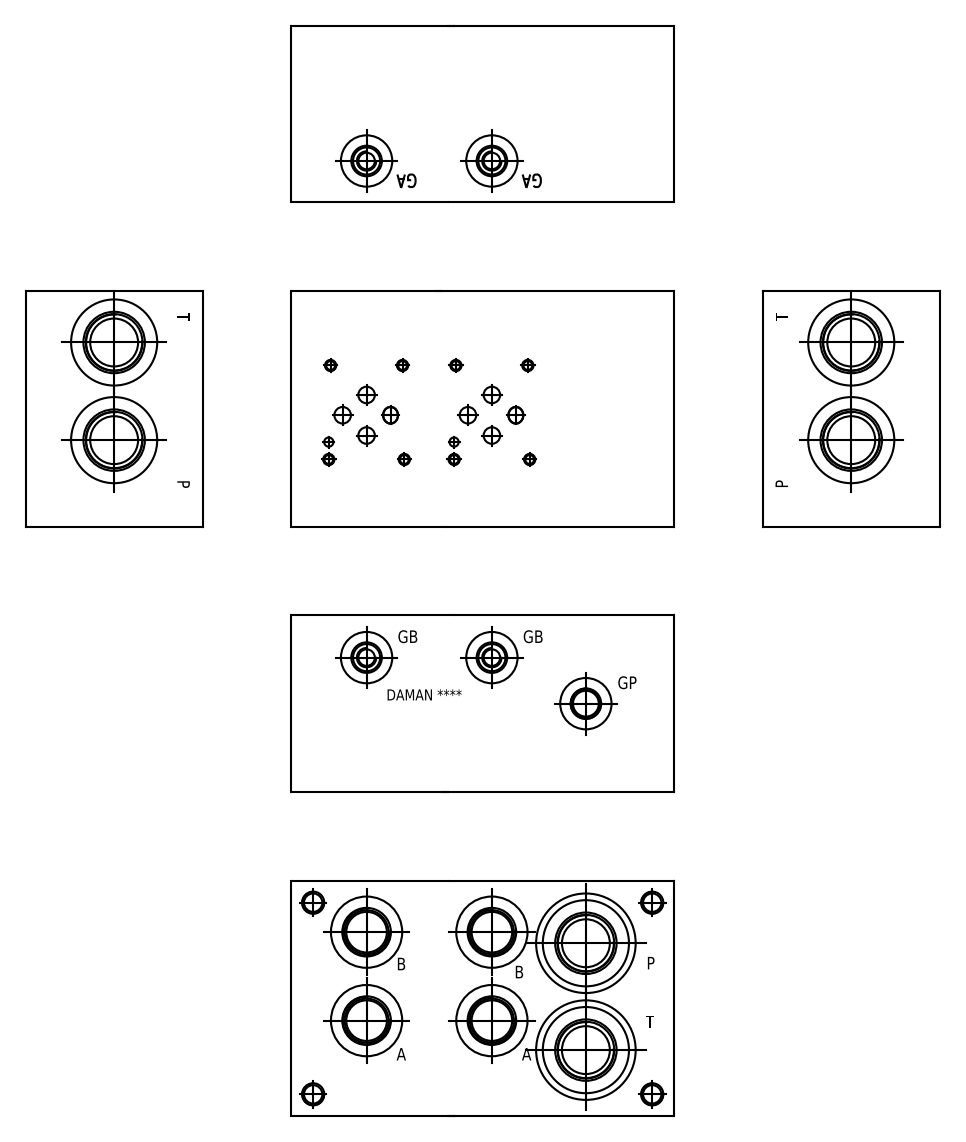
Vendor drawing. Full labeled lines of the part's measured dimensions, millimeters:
Part name (STEP PRODUCT): AD03PB022B
STEP written by: Autodesk Inventor 2009 (AUTOMOTIVE_DESIGN)
Units: millimetres
Bodies: 1 solid, 226 faces (48 planar, 89 cylindrical, 89 other)
Overall size (bounding box): 165.1 × 101.6 × 76.2
Volume: 1 087 000 mm³ · Surface area: 108 531 mm²
Round holes (diameter × count): ⌀7.14 ×10, ⌀3.78 ×8, ⌀4.83 ×8, ⌀13.16 ×5, ⌀22.12 ×5, ⌀9.52 ×4, ⌀11.68 ×4, ⌀20.62 ×4, ⌀20.95 ×4, ⌀24.41 ×4, ⌀26.44 ×4, ⌀30.68 ×4
Round bosses / shafts (diameter × count): ⌀18.92 ×2, ⌀7.92 ×2, ⌀11.68 ×1
Main face-to-face distances: 101.6, 76.2, 165.1, 0.79, 164.31, 5.56, 70.64, 4.77, 75.41, 100.81
Hole centre spacings: 53.97, 13.52, 13.54, 19.95, 22.05, 33.55, 40.5, 51.45
